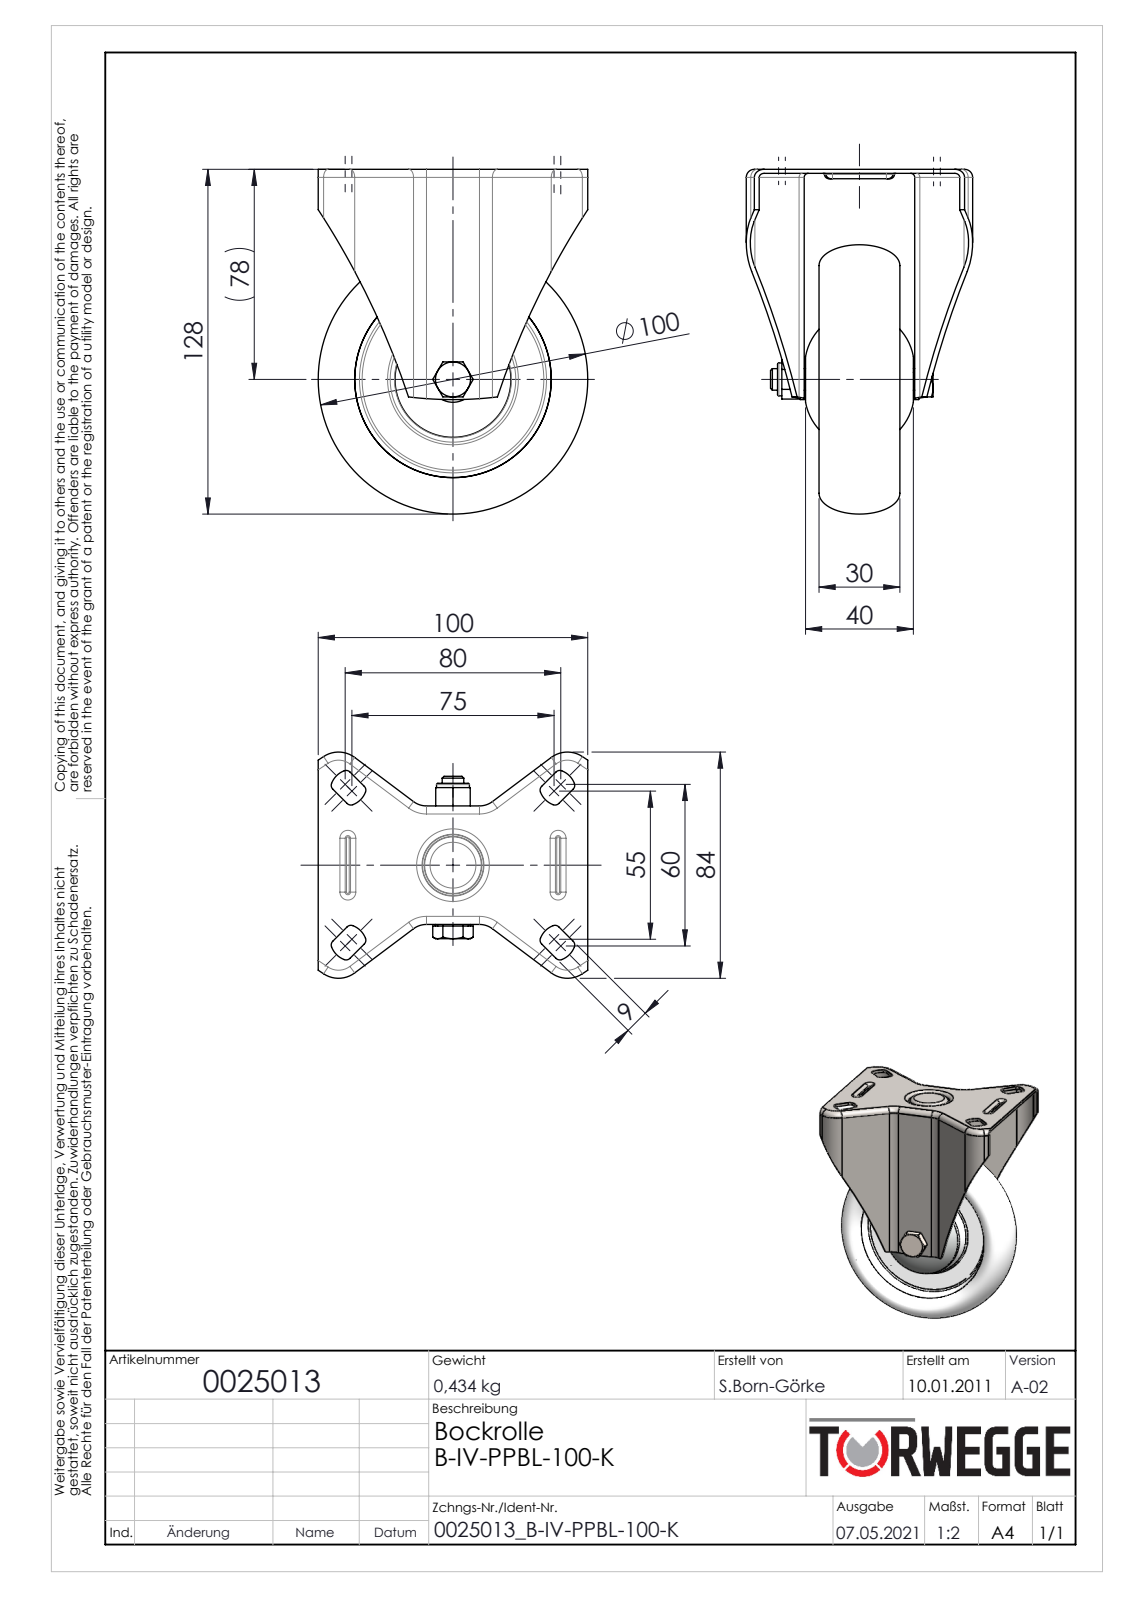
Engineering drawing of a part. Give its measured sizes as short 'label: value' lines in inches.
name: 0025013
written by: SolidWorks 2020 (AUTOMOTIVE_DESIGN)
unit: in
bodies: 12 solids, 396 faces (88 planar, 140 cylindrical, 168 other)
size: 5.039 × 3.937 × 3.307
volume: 11.4 in³; area: 165.3 in²
holes: 1× ⌀0.262, 1× ⌀0.315, 1× ⌀0.327, 1× ⌀0.827, 1× ⌀1.299, 1× ⌀1.378
bosses: 1× ⌀1.142, 1× ⌀0.591, 1× ⌀0.512, 1× ⌀0.48
rounds: 24× R0.079, 10× R0.059, 10× R0.118, 8× R0.02, 8× R0.318, 4× R0.315, 4× R0.335, 4× R0.374
face distances: 0.059, 0.735, 0.925, 0.748, 0.984, 0.794, 0.344, 1.673, 0.689, 0.676
